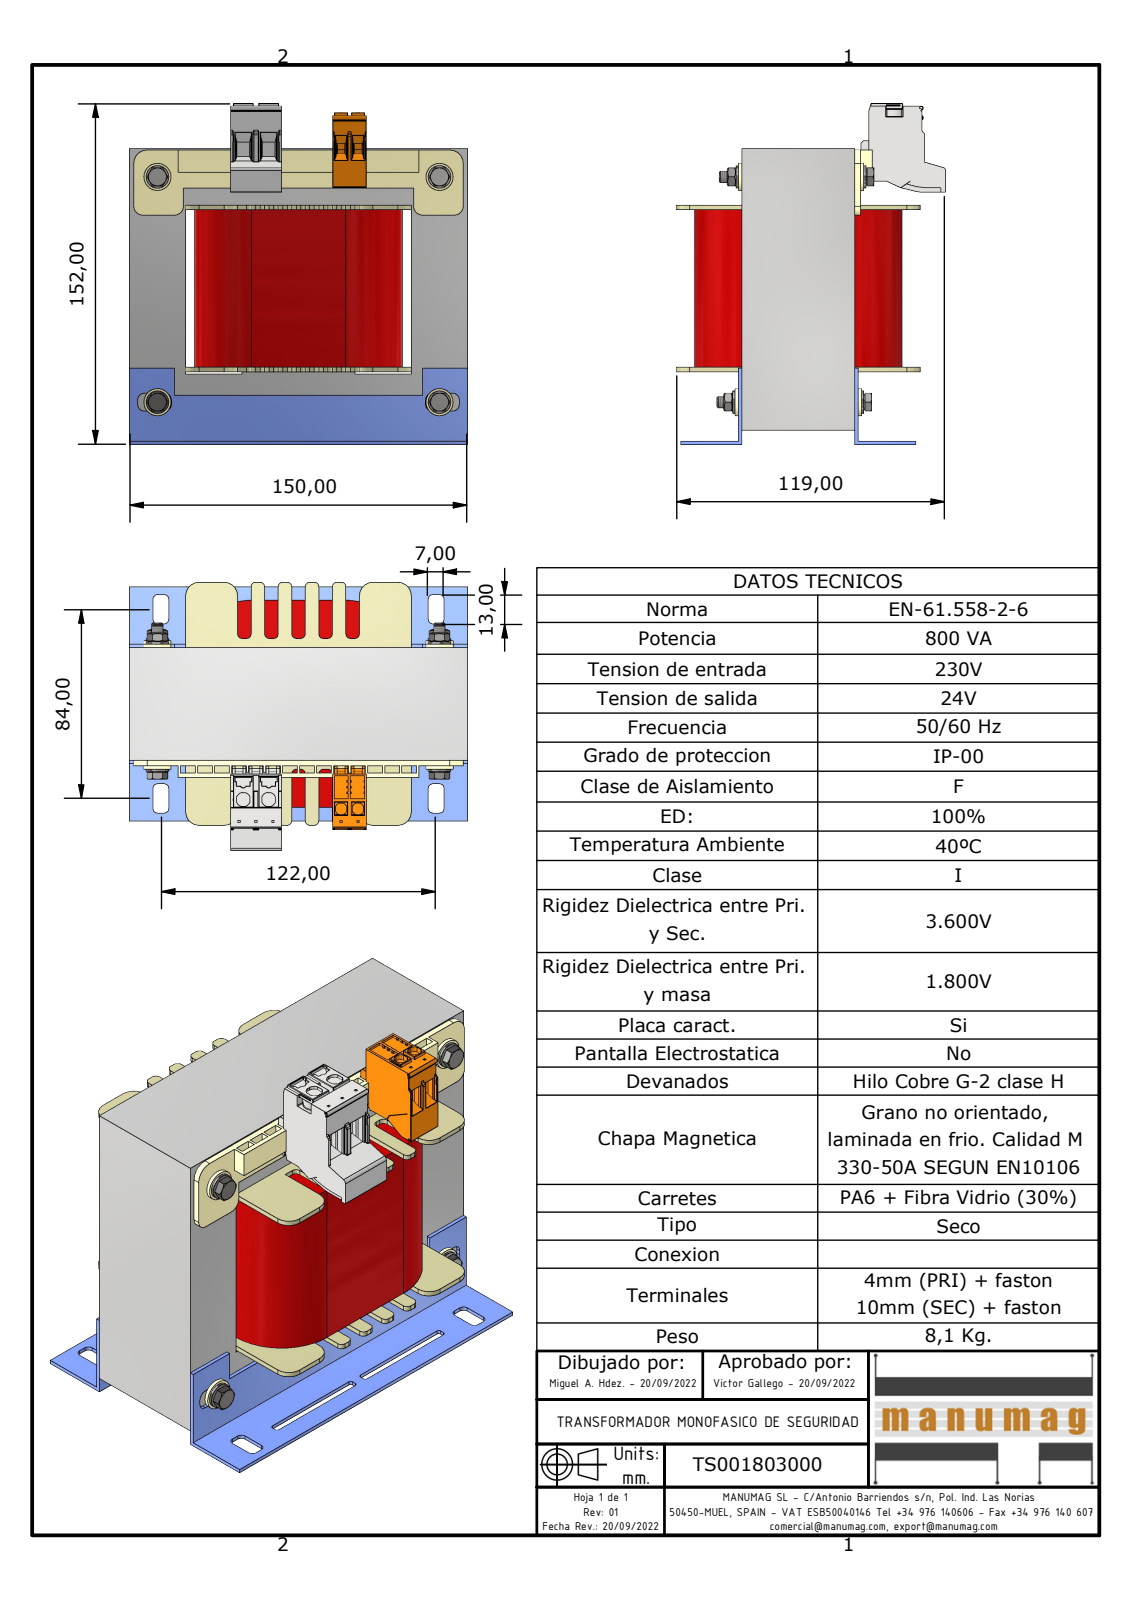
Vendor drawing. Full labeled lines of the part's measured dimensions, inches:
Part name (STEP PRODUCT): TS001803000; EI150 x 125 - 50 (RC50); AF50DIN; centrador M5 (+7 more)
STEP written by: Autodesk Inventor 2023 (AUTOMOTIVE_DESIGN)
Units: inches
Bodies: 31 solids, 4190 faces (3354 planar, 596 cylindrical, 240 other)
Overall size (bounding box): 5.969 × 5.906 × 4.695
Volume: 73.84 in³ · Surface area: 327.3 in²
Round holes (diameter × count): ⌀0.163 ×4, ⌀0.197 ×4, ⌀0.209 ×4, ⌀0.315 ×4
Round bosses / shafts (diameter × count): ⌀0.472 ×4, ⌀0.394 ×4, ⌀0.264 ×4, ⌀0.232 ×4, ⌀0.18 ×4
Partial cylindrical surfaces — rounded edges, fillets, slot ends (radius × count): R0.006 ×98, R0.008 ×85, R0.079 ×53, R0.012 ×37, R0.039 ×22, R0.004 ×14, R0.02 ×14, R0.236 ×10
Main face-to-face distances: 1.969, 3.937, 0.984, 4.921, 0.059, 2.953, 0.827, 2.795, 0.079, 2.913
Hole centre spacings: 3.937, 4.921, 6.302
